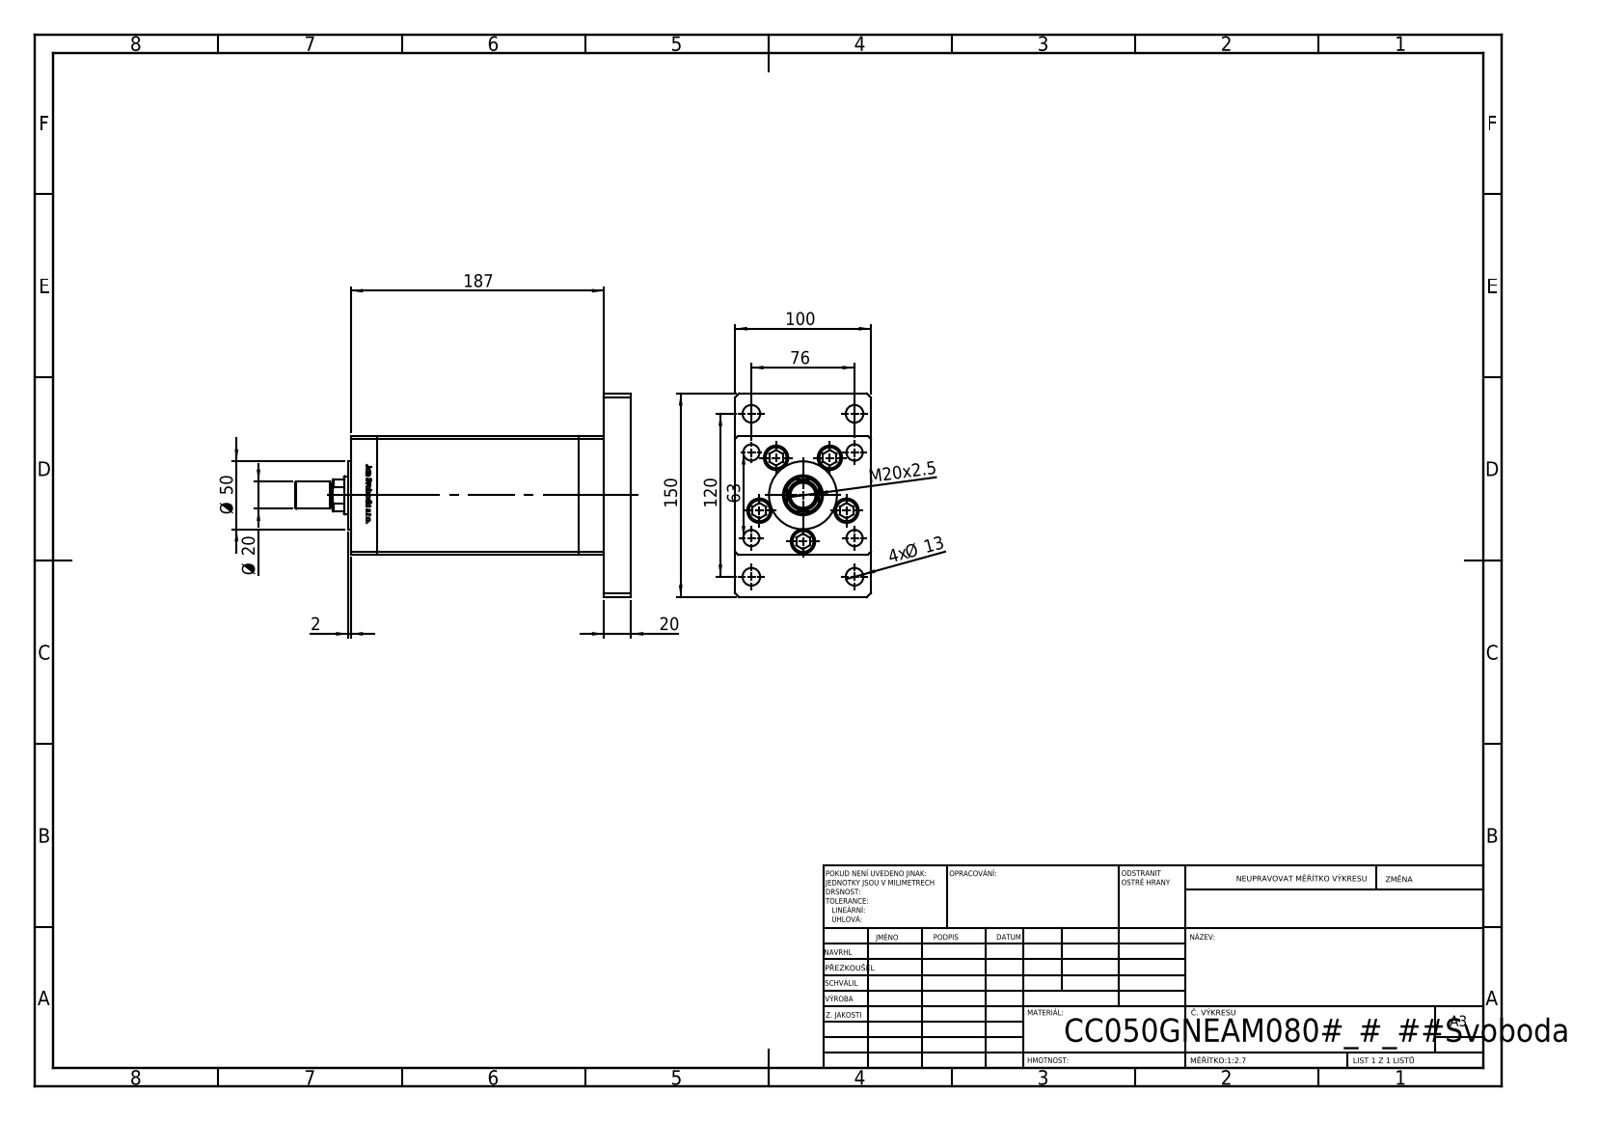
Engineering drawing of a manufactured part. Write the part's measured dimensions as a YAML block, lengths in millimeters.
part_name: "V220C_VC_G; V220C_F; V220C BACK_G; V220CC_MALE_METRIC (+3 more)"
step_written_by: "SolidWorks 2019 (CONFIG_CONTROL_DESIGN)"
units: millimeters
bodies: {solids: 20, faces: 1324, planar: 521, cylindrical: 191, other: 612}
overall_size: [247.5, 150, 100]
volume: 1706000
surface_area: 259133
round_holes:
  - {diameter: 12, count: 9}
  - {diameter: 13.5, count: 5}
  - {diameter: 18, count: 5}
  - {diameter: 13, count: 4}
  - {diameter: 17, count: 4}
  - {diameter: 2, count: 2}
  - {diameter: 13.16, count: 2}
  - {diameter: 18.5, count: 1}
  - {diameter: 28, count: 1}
  - {diameter: 29.5, count: 1}
  - {diameter: 68, count: 1}
round_bosses_or_shafts:
  - {diameter: 8, count: 9}
  - {diameter: 17, count: 5}
  - {diameter: 50, count: 1}
  - {diameter: 20, count: 1}
  - {diameter: 18, count: 1}
partial_cylinders:
  - {radius: 0.93, count: 2}
  - {radius: 13.5, count: 1}
face_to_face_distances: [19, 100, 167.5, 87, 148.5, 20, 187.5, 39, 206.5, 186.5]
hole_center_spacings: [34, 28.5, 49.36, 71.02, 76, 81.17, 91.5, 118.95]
